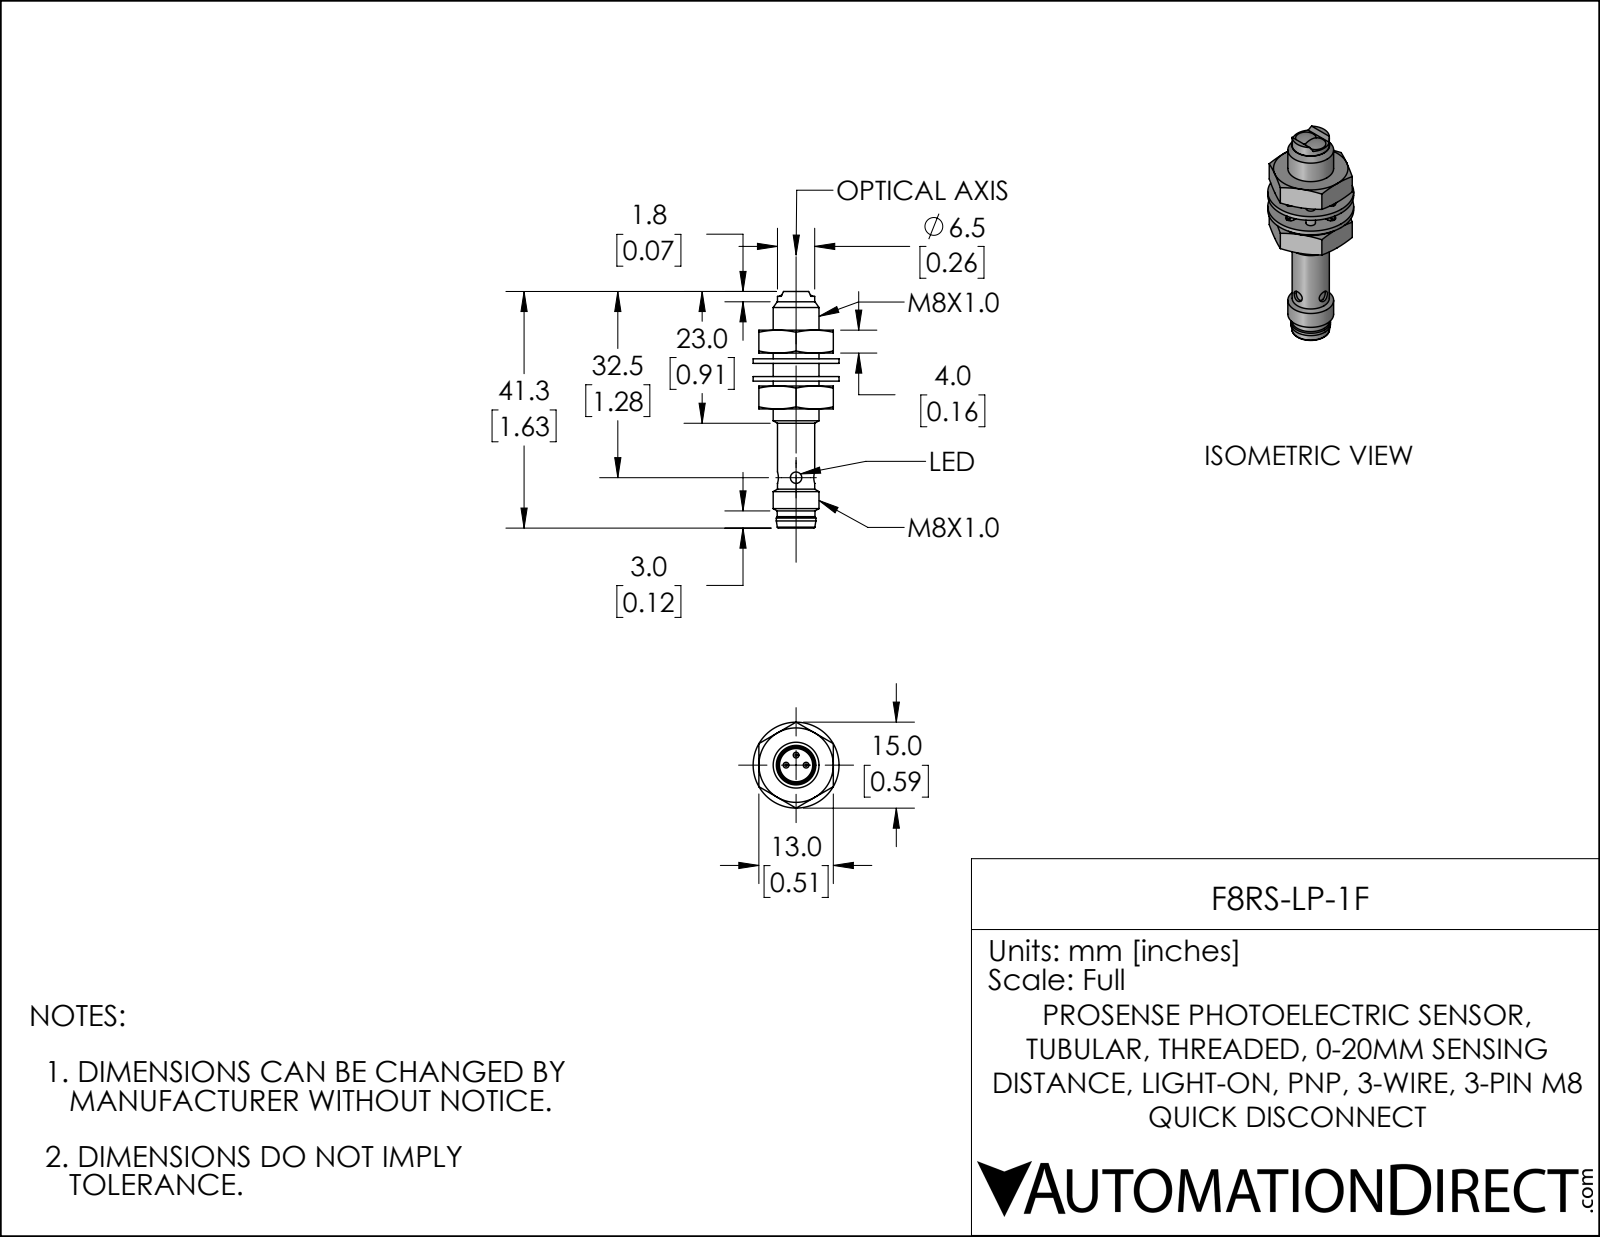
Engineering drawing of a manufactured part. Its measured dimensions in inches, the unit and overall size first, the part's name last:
Units: inches
Overall size (bounding box): 1.626 × 0.591 × 0.591
Round holes (diameter × count): ⌀0.079 ×2, ⌀0.228 ×1, ⌀0.272 ×1
Round bosses / shafts (diameter × count): ⌀0.039 ×3, ⌀0.591 ×1, ⌀0.315 ×1, ⌀0.272 ×1, ⌀0.26 ×1, ⌀0.256 ×1
Partial cylindrical surfaces — rounded edges, fillets, slot ends (radius × count): R0.032 ×8, R0.109 ×1, R0.165 ×1
Main face-to-face distances: 0.122, 0.031, 0.512, 0.384, 0.157, 0.154, 0.091, 0.033, 0.065, 0.197
Volume: 0.162 in³ · Surface area: 4.169 in²
Bodies: 5 solids, 157 faces (63 planar, 54 cylindrical, 40 other)
Part name (STEP PRODUCT): F8RS-LP-1F
STEP written by: SolidWorks 2019 (CONFIG_CONTROL_DESIGN)
